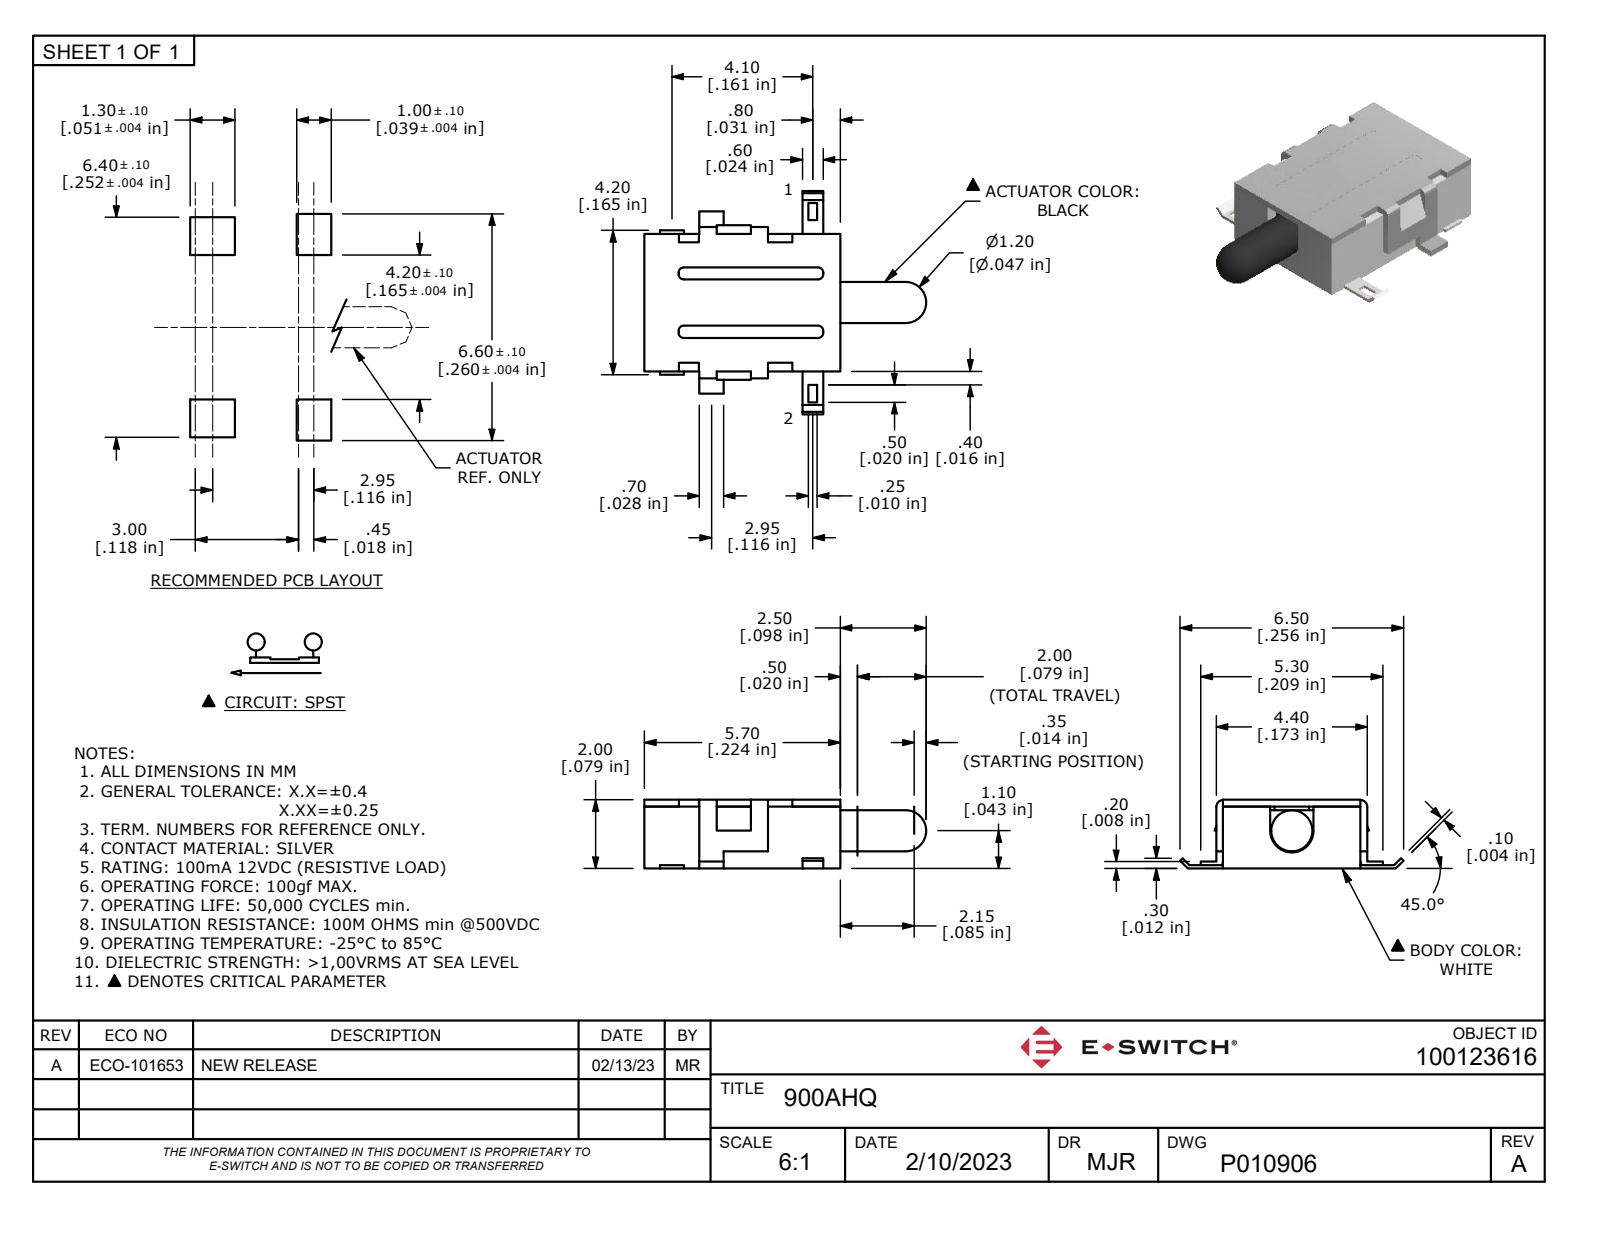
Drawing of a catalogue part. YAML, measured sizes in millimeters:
part_name: "900AGQ"
step_written_by: "Autodesk Inventor 2022 (AUTOMOTIVE_DESIGN)"
units: millimeters
bodies: {solids: 1, faces: 148, planar: 123, cylindrical: 20, other: 5}
overall_size: [8.2, 6.5, 2]
volume: 30
surface_area: 184
round_holes:
  - {diameter: 0.3, count: 4}
round_bosses_or_shafts:
  - {diameter: 1.2, count: 1}
partial_cylinders:
  - {radius: 0.2, count: 8}
  - {radius: 0.2, count: 4}
  - {radius: 0.6, count: 1}
face_to_face_distances: [2, 1.5, 1.7, 0.4, 1.8, 1.3, 1.4, 3.7, 1.6, 0.5]
hole_center_spacings: [2, 3.5, 4]
